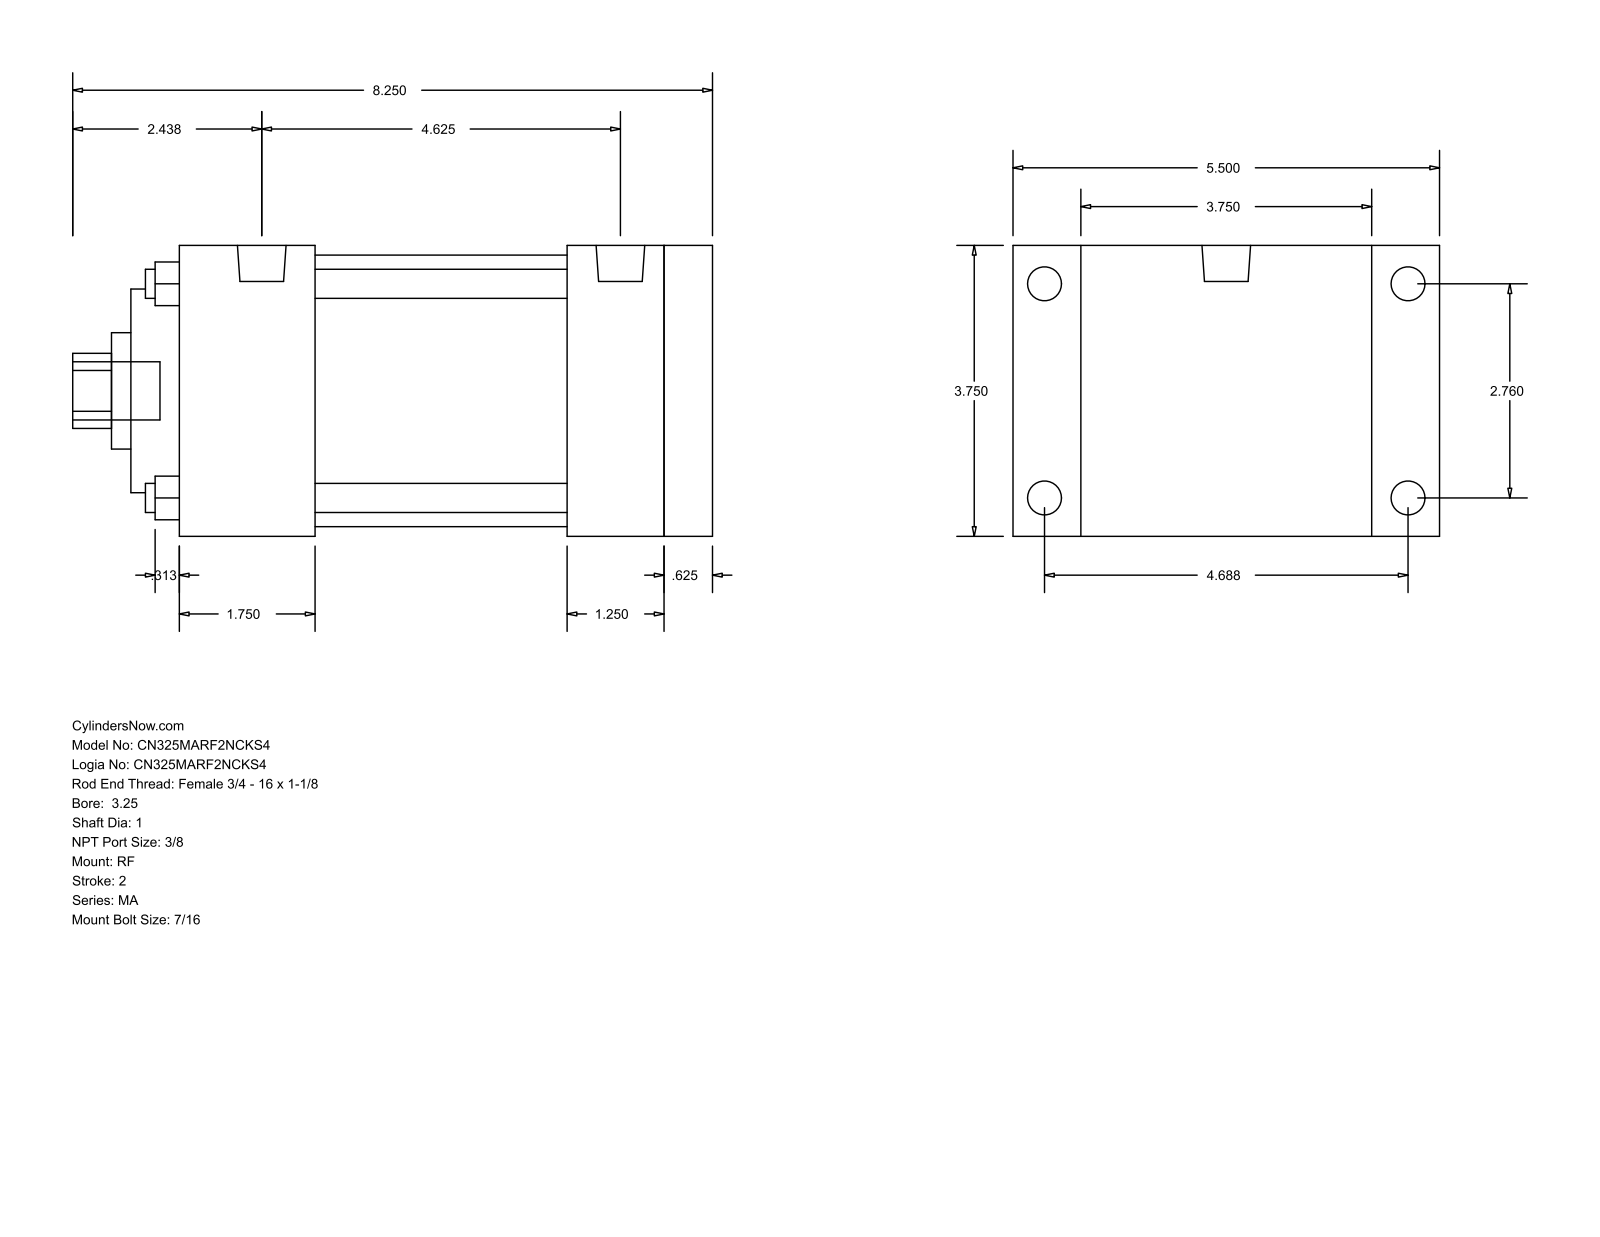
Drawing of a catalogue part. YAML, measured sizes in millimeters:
part_name: "MA_RF__0325_1"
step_written_by: "GSSL Pune (CONFIG_CONTROL_DESIGN)"
units: millimeters
bodies: {solids: 0, faces: 94, planar: 65, cylindrical: 29, other: 0}
overall_size: [209.55, 139.7, 95.25]
round_holes:
  - {diameter: 9.53, count: 4}
  - {diameter: 25.4, count: 1}
  - {diameter: 38.1, count: 1}
  - {diameter: 66.67, count: 1}
  - {diameter: 88.9, count: 1}
round_bosses_or_shafts:
  - {diameter: 11.11, count: 8}
  - {diameter: 15.93, count: 2}
  - {diameter: 19.05, count: 1}
partial_cylinders:
  - {radius: 12.29, count: 1}
face_to_face_distances: [95.24, 174.63, 15.87, 158.76, 22.23, 117.47, 127.01, 31.75, 47.62, 44.46]
hole_center_spacings: [49.57, 70.1, 99.14]
